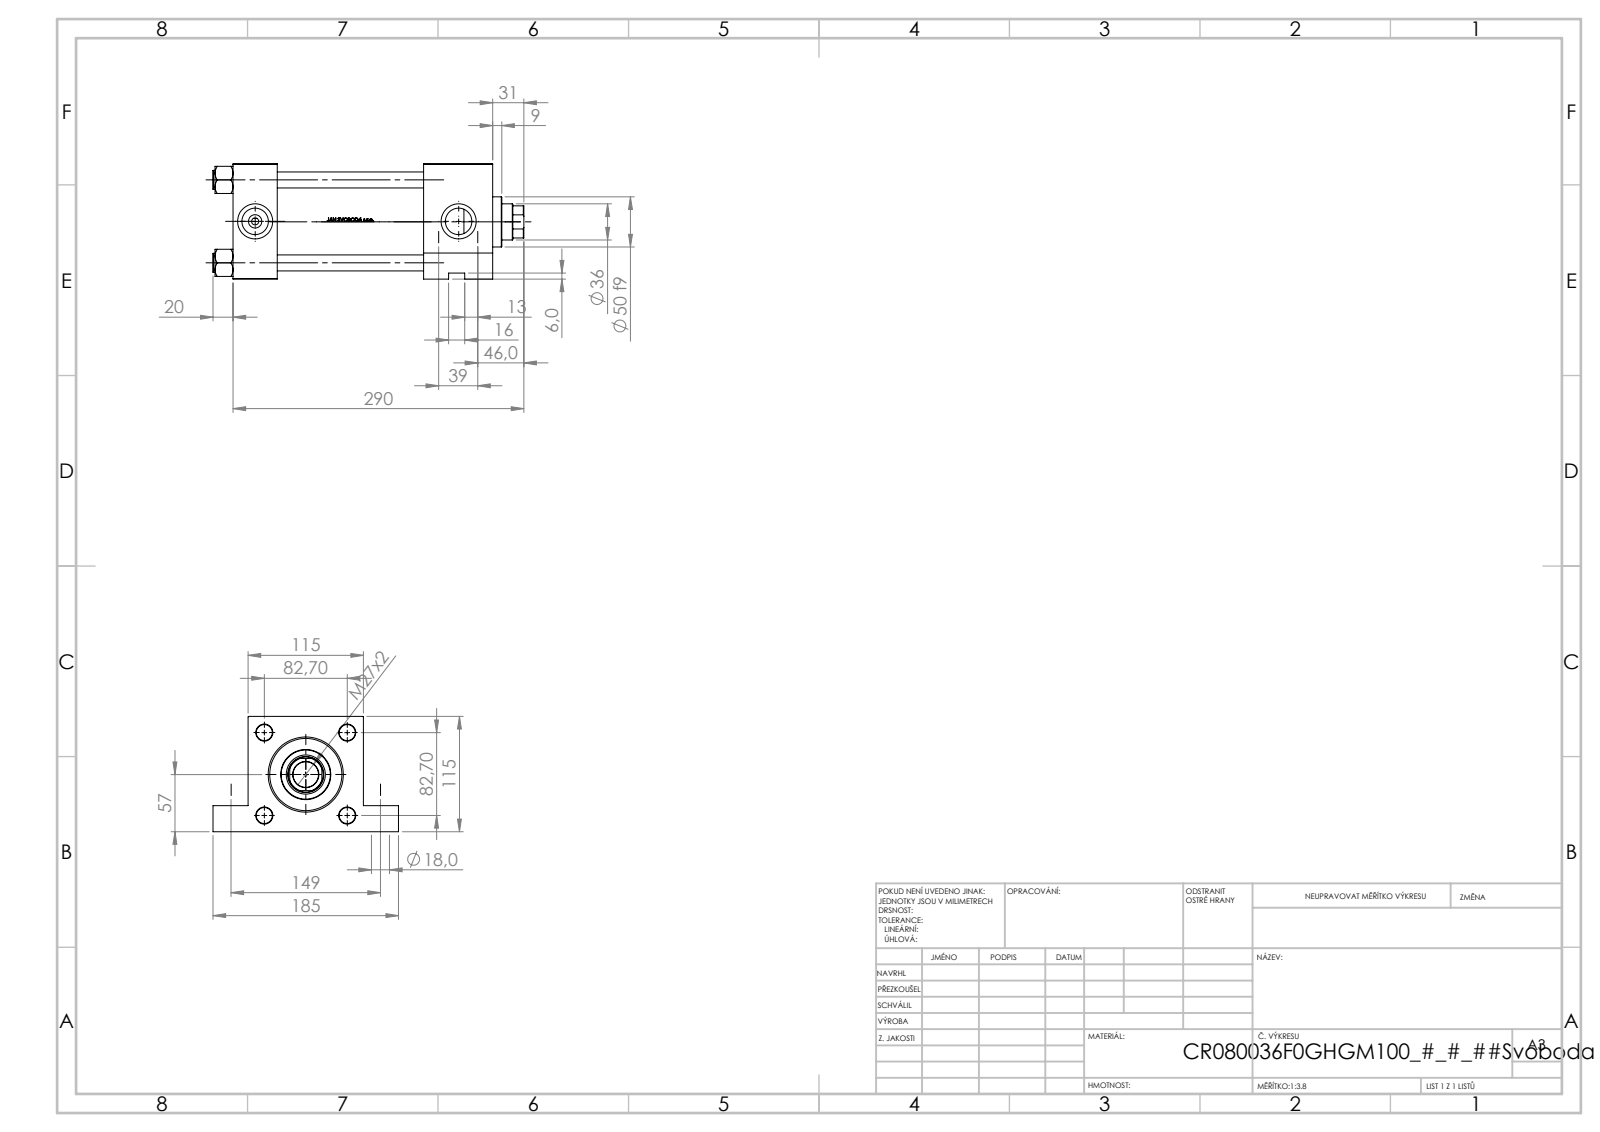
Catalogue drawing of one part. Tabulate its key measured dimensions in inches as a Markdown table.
| quantity | value |
| --- | --- |
| part name | V215CR_F_Body; V215CR_F_TYCINKA; V215_VC_A; NUT_M5_F (+1 more) |
| STEP written by | SolidWorks 2019 (CONFIG_CONTROL_DESIGN) |
| units | inches |
| bodies | 11 solids, 1151 faces (485 planar, 126 cylindrical, 540 other) |
| overall size | 12.205 × 7.283 × 4.528 |
| volume | 127.6 in³ |
| surface area | 543.2 in² |
| round holes (diameter × count) | 0.63 × 4, 0.276 × 2, 0.709 × 2, 0.709 × 2, 1.041 × 2, 1.378 × 2, 1.004 × 1, 1.417 × 1, 1.535 × 1, 2.402 × 1, 2.835 × 1, 3.15 × 1 |
| round bosses / shafts (diameter × count) | 0.748 × 4, 3.386 × 1, 1.969 × 1 |
| partial cylindrical surfaces (radius × count) | 0.689 × 1 |
| main face-to-face distances | 4.528, 1.732, 8.465, 10.197, 7.48, 5.748, 2.717, 3.937, 9.067, 7.335 |
| hole center spacings | 3.256, 1.535, 2.289, 2.316, 4.605, 5.866, 6.064, 7.992 |
